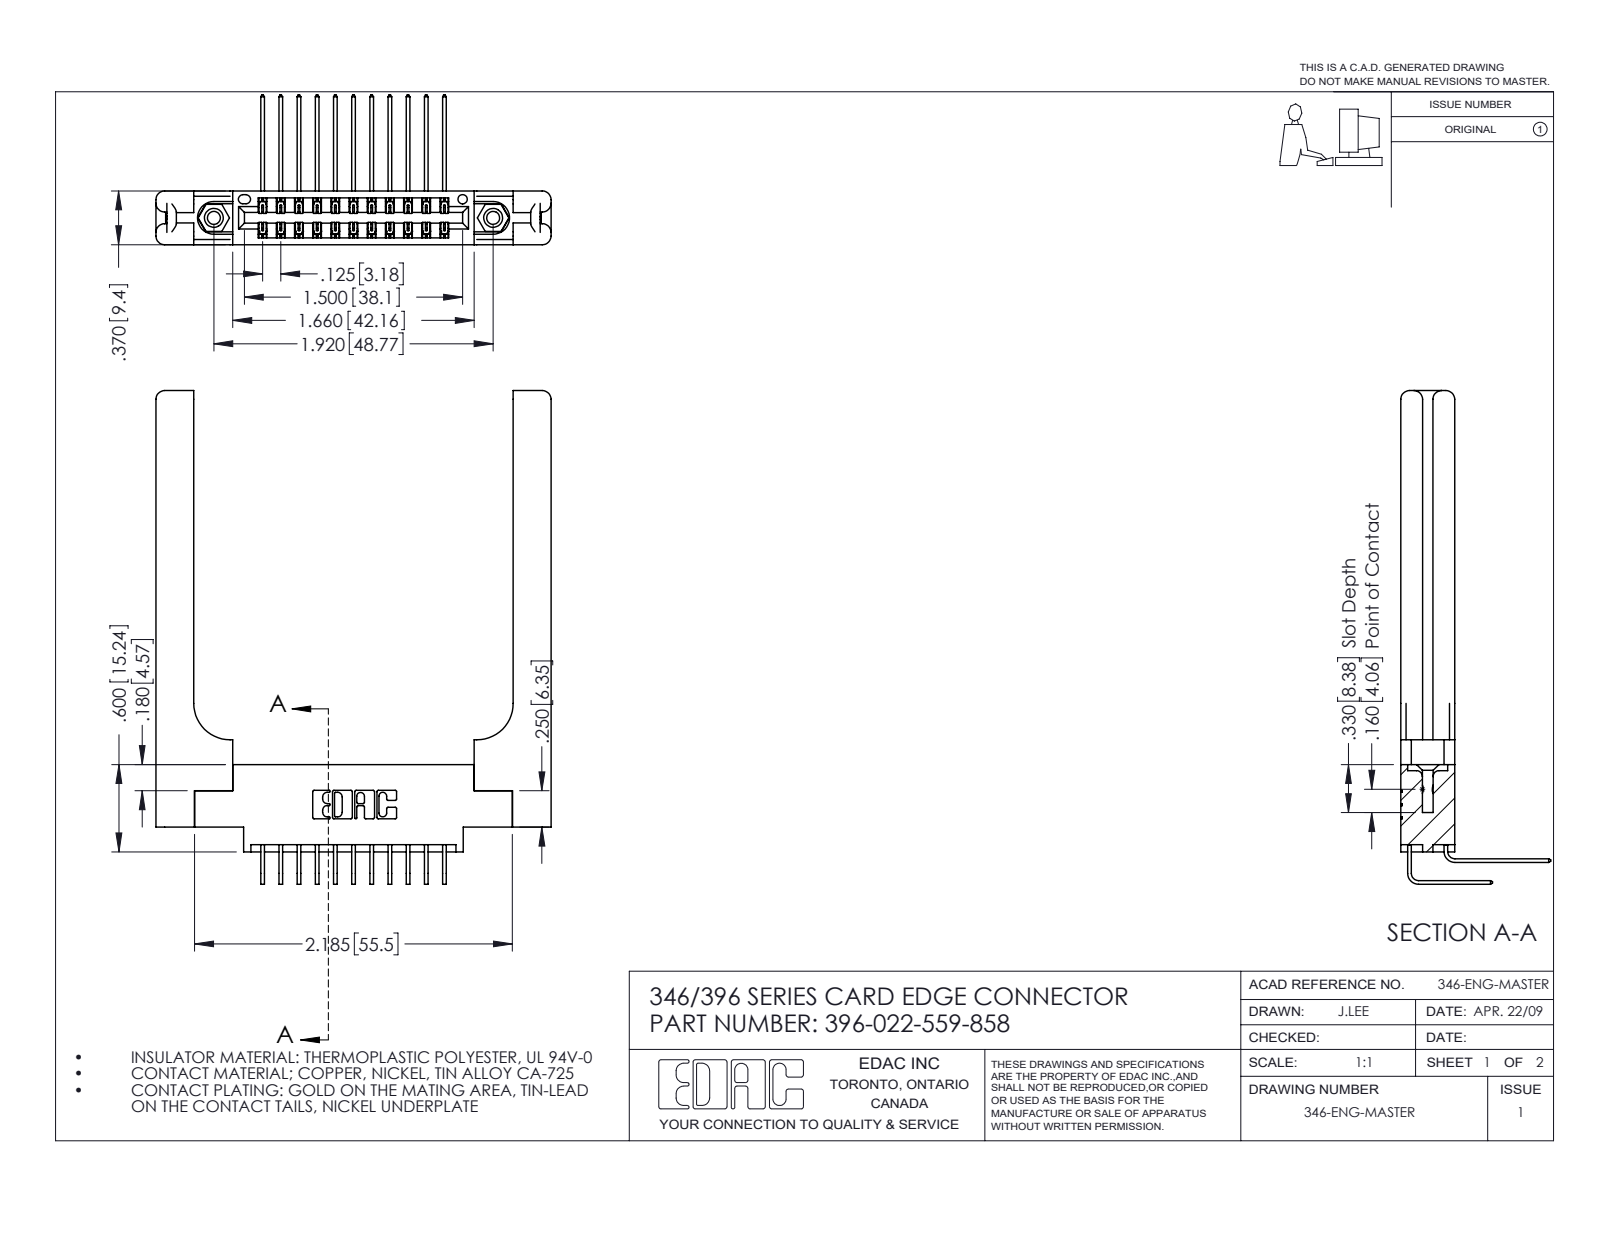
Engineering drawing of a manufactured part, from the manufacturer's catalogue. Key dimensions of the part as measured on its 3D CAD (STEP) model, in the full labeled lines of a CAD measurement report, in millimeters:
Part name (STEP PRODUCT): 346 Part_0.170 Offset - 0.156 Dia-TH; 346-220-058_345-220-058; 345-250-001_345-250-001-102; 345-292-001_558 559 Tail - 1 (+2 more)
STEP written by: SolidWorks 2016 (CONFIG_CONTROL_DESIGN)
Units: millimetres
Bodies: 27 solids, 1570 faces (1042 planar, 468 cylindrical, 60 other)
Overall size (bounding box): 86.2 × 69 × 26.2
Volume: 13 900 mm³ · Surface area: 14 150 mm²
Round holes (diameter × count): ⌀2.3 ×2, ⌀3.2 ×2, ⌀4 ×2, ⌀1.6 ×1
Round bosses / shafts (diameter × count): ⌀3.9 ×2
Partial cylindrical surfaces — rounded edges, fillets, slot ends (radius × count): R0.2 ×33, R0.3 ×22, R1.5 ×16, R0.2 ×6, R0.8 ×6, R0.7 ×3, R0.4 ×2, R0.6 ×2
Main face-to-face distances: 9.4, 3.8, 1.8, 1.2, 3.8, 8.2, 5.6, 2.6, 4.4, 0.6
Hole centre spacings: 6.2, 43.6, 48.8
